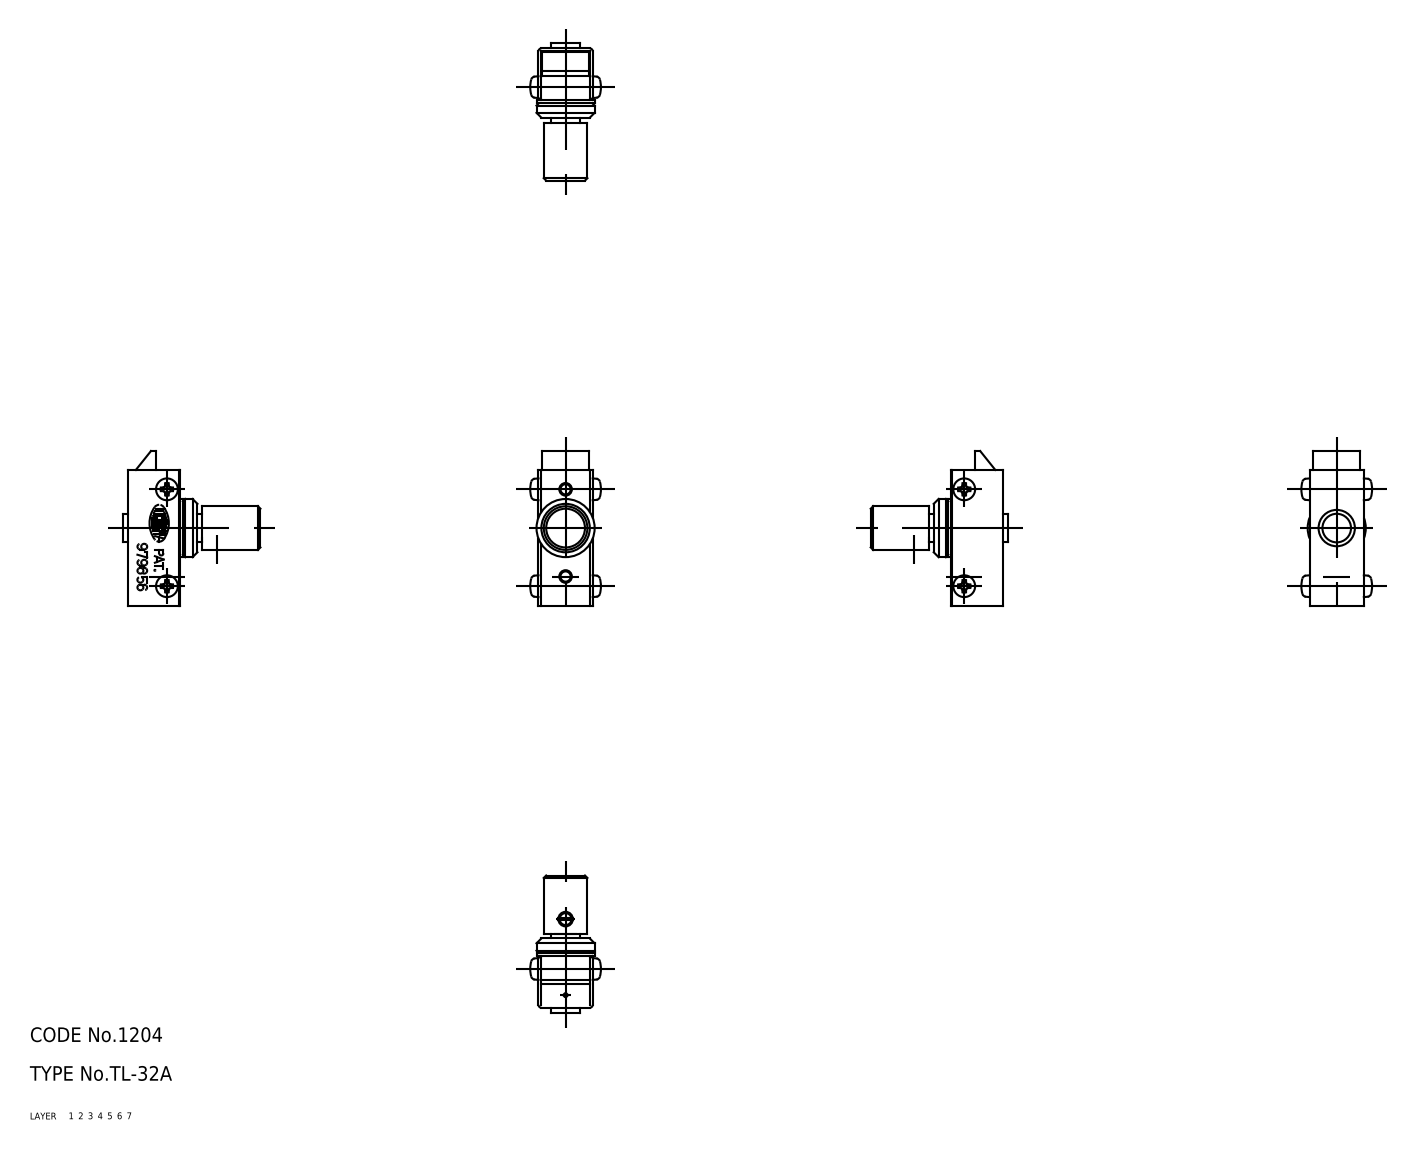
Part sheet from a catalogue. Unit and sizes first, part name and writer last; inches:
Units: inches
Overall size (bounding box): 1.26 × 1.118 × 0.573
Volume: 0.221 in³ · Surface area: 9.055 in²
Bodies: 13 solids, 234 faces (0 planar, 0 cylindrical, 234 other)
Part name (STEP PRODUCT): screw_2; screw_1; washer; spring (+7 more)
STEP written by: CADfix (AUTOMOTIVE_DESIGN)
